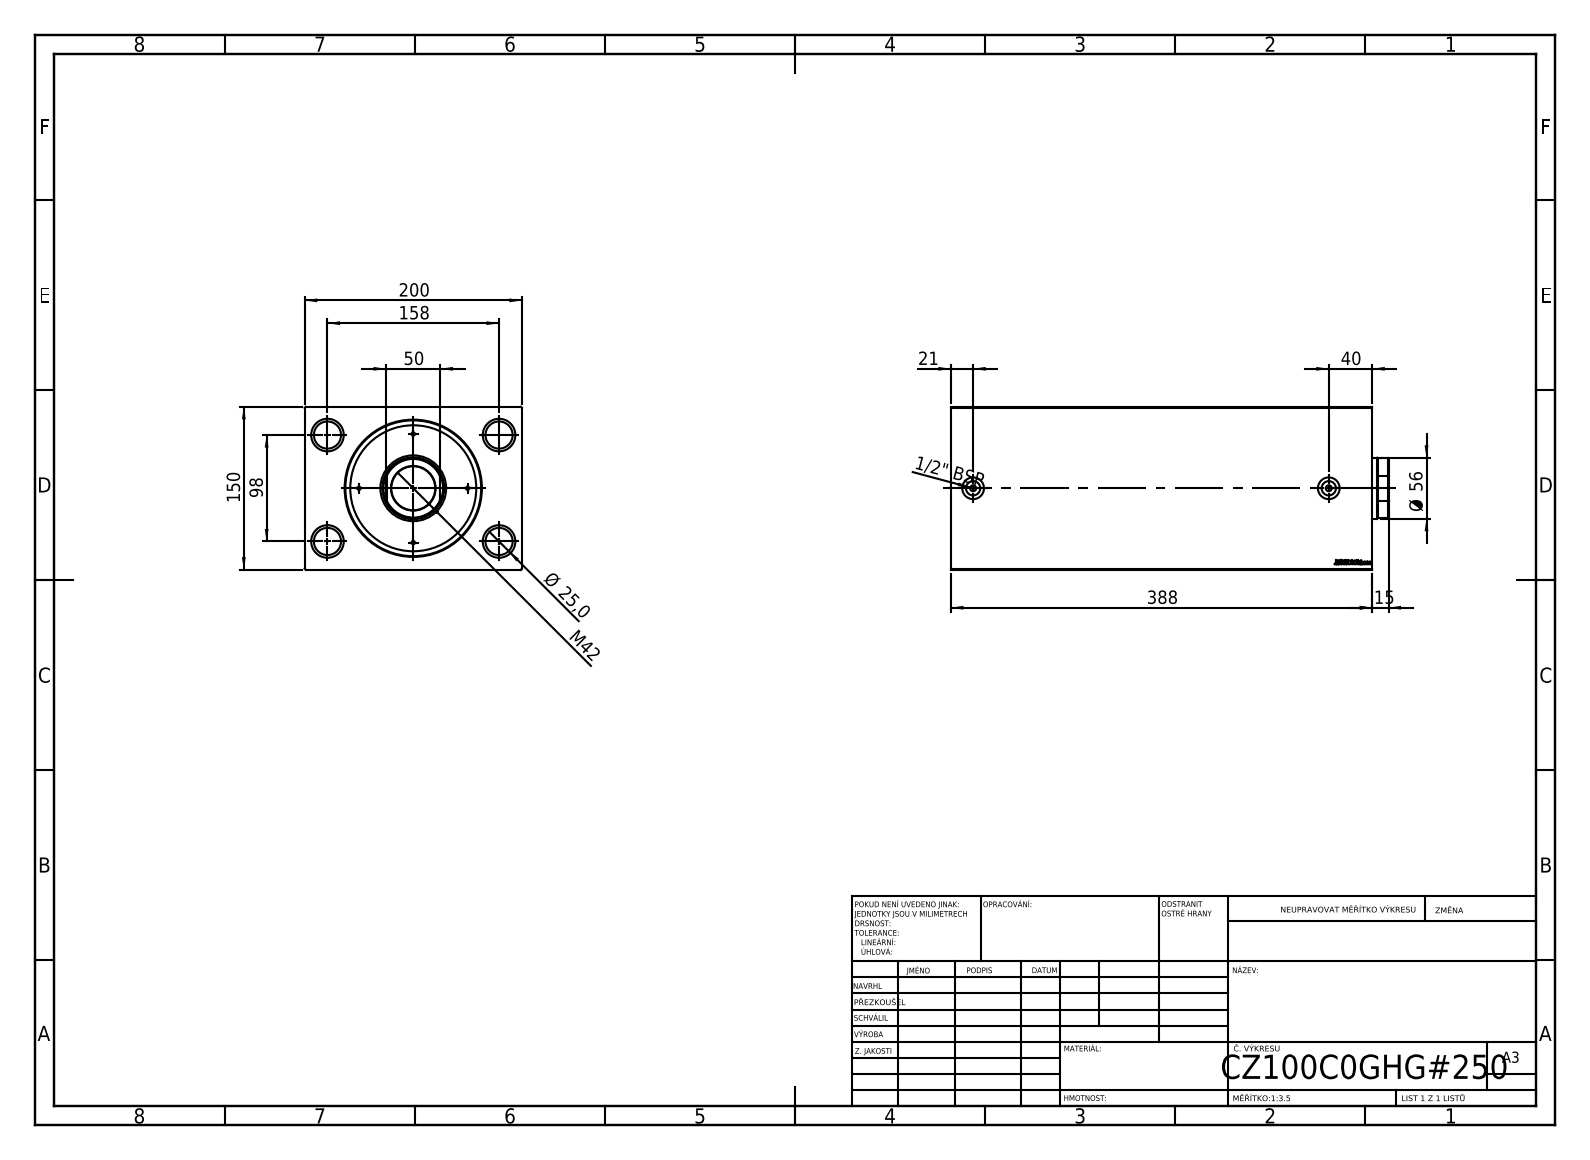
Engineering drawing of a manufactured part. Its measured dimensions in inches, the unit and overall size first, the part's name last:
Units: inches
Overall size (bounding box): 15.276 × 7.874 × 5.906
Round holes (diameter × count): ⌀0.984 ×4, ⌀1.181 ×4, ⌀0.217 ×2, ⌀0.315 ×2, ⌀0.518 ×2, ⌀0.787 ×2, ⌀1.417 ×1, ⌀3.937 ×1, ⌀4.921 ×1
Main face-to-face distances: 5.906, 7.874, 15.276, 13.965, 1.311, 0.591, 13.374, 14.685, 0.407, 14.869
Hole centre spacings: 3.66, 3.858, 6.22, 7.32, 12.106, 12.894
Volume: 488.4 in³ · Surface area: 874.2 in²
Bodies: 1 solid, 825 faces (397 planar, 46 cylindrical, 382 other)
STEP written by: SolidWorks 2019 (CONFIG_CONTROL_DESIGN)
